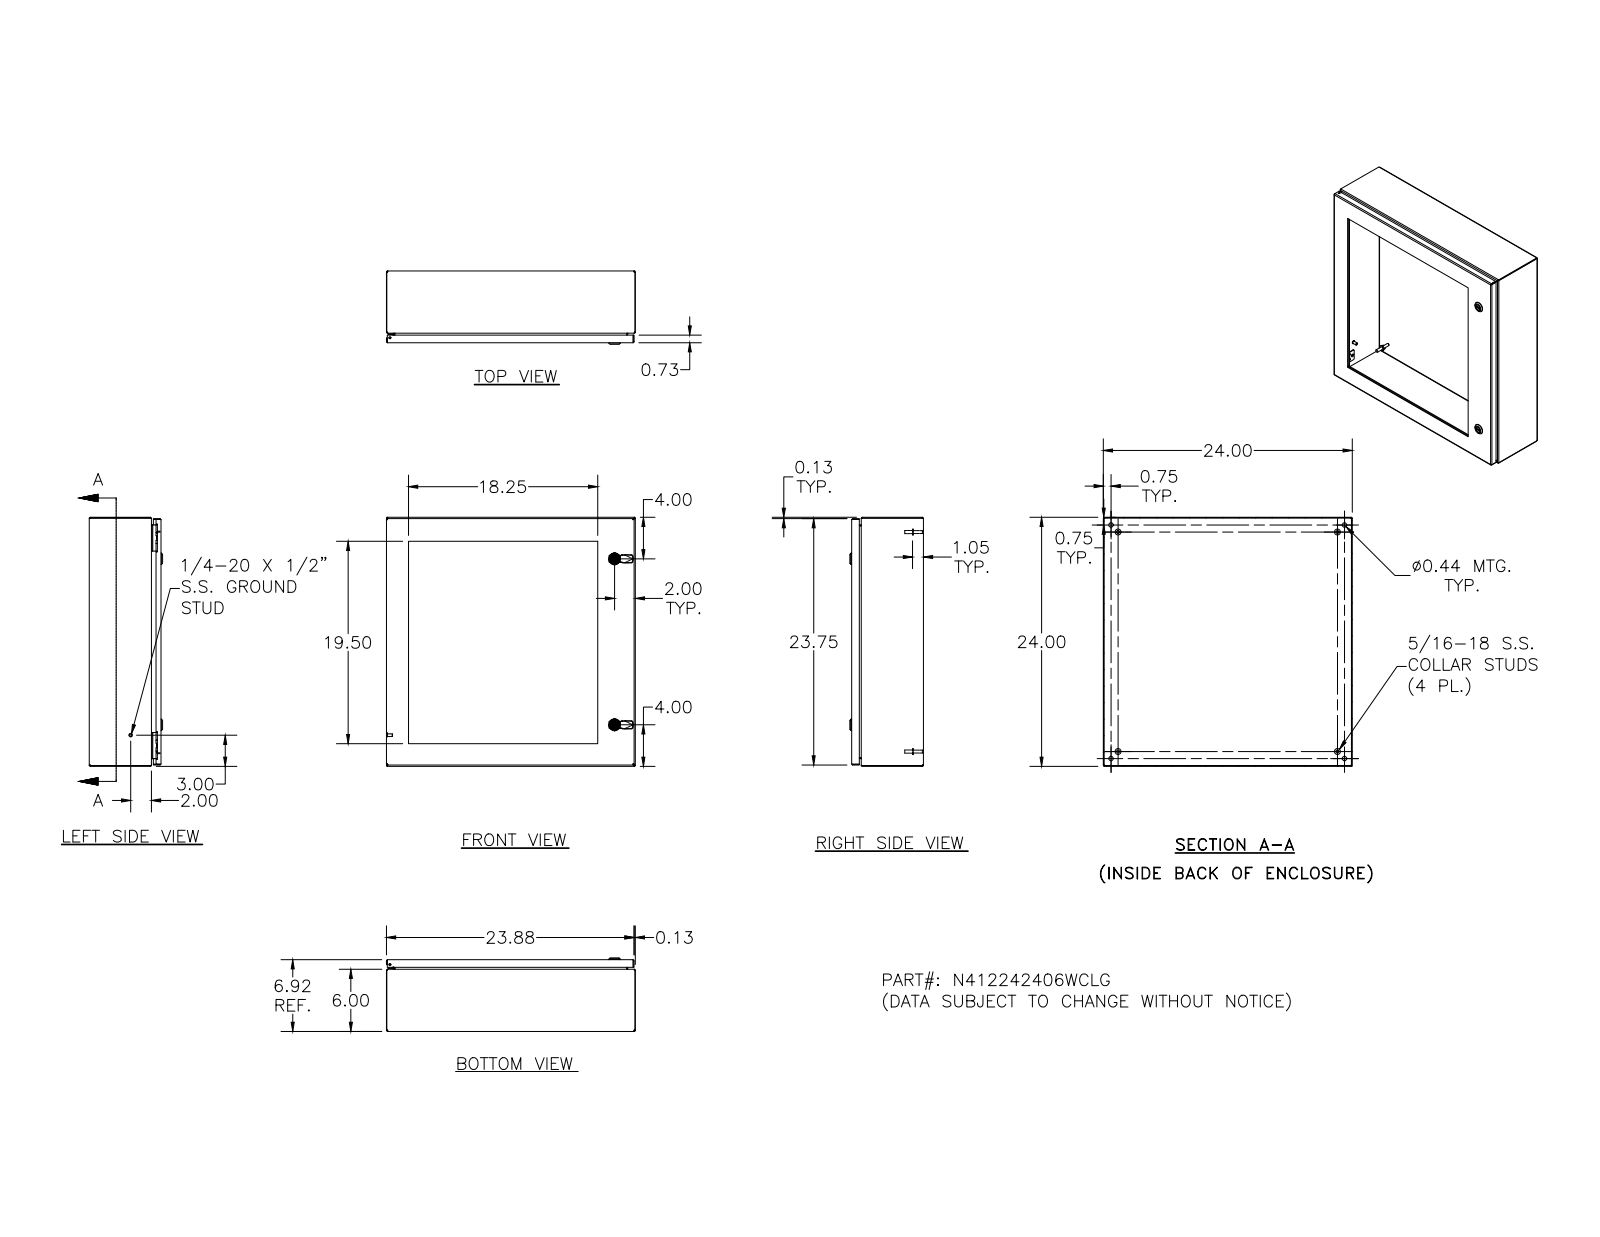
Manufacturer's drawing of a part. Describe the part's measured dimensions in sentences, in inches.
The part is named "N412242406WCLG". Its 3-D file was written by "SolidWorks 2018 (AUTOMOTIVE_DESIGN)". It is 84 solids with 2510 faces: 971 planar, 762 cylindrical and 777 other. Overall it measures 24 by 24 by 7.075 inches. Its volume is 221.9 cubic inches and its surface area 4 176 square inches. Round holes: 22 of diameter 0.156, 20 of diameter 0.281, 5 of diameter 0.188, 4 of diameter 0.093, 4 of diameter 0.152, 4 of diameter 0.167, 4 of diameter 0.172, 4 of diameter 0.437, 2 of diameter 0.197, 2 of diameter 0.315, 2 of diameter 0.394, 2 of diameter 0.402. Round bosses or shafts: 20 of diameter 0.337, 20 of diameter 0.19, 10 of diameter 0.25, 4 of diameter 0.563, 4 of diameter 0.36, 4 of diameter 0.32, 4 of diameter 0.3, 4 of diameter 0.275. Partial cylindrical surfaces (rounded edges, fillets, slot ends): 54 of radius 0.012, 34 of radius 0.031, 26 of radius 0.05, 24 of radius 0.105, 23 of radius 0.02, 18 of radius 0.016, 16 of radius 0.125, 8 of radius 0.032. The main face-to-face distances are 0.074, 6.843, 6.769, 23.926, 0.25, 6.593, 6.519, 24, 23.852, 6.917. The hole center spacings are 4, 8, 21.132, 12, 20, 22.239, 20.75, 6.221.
